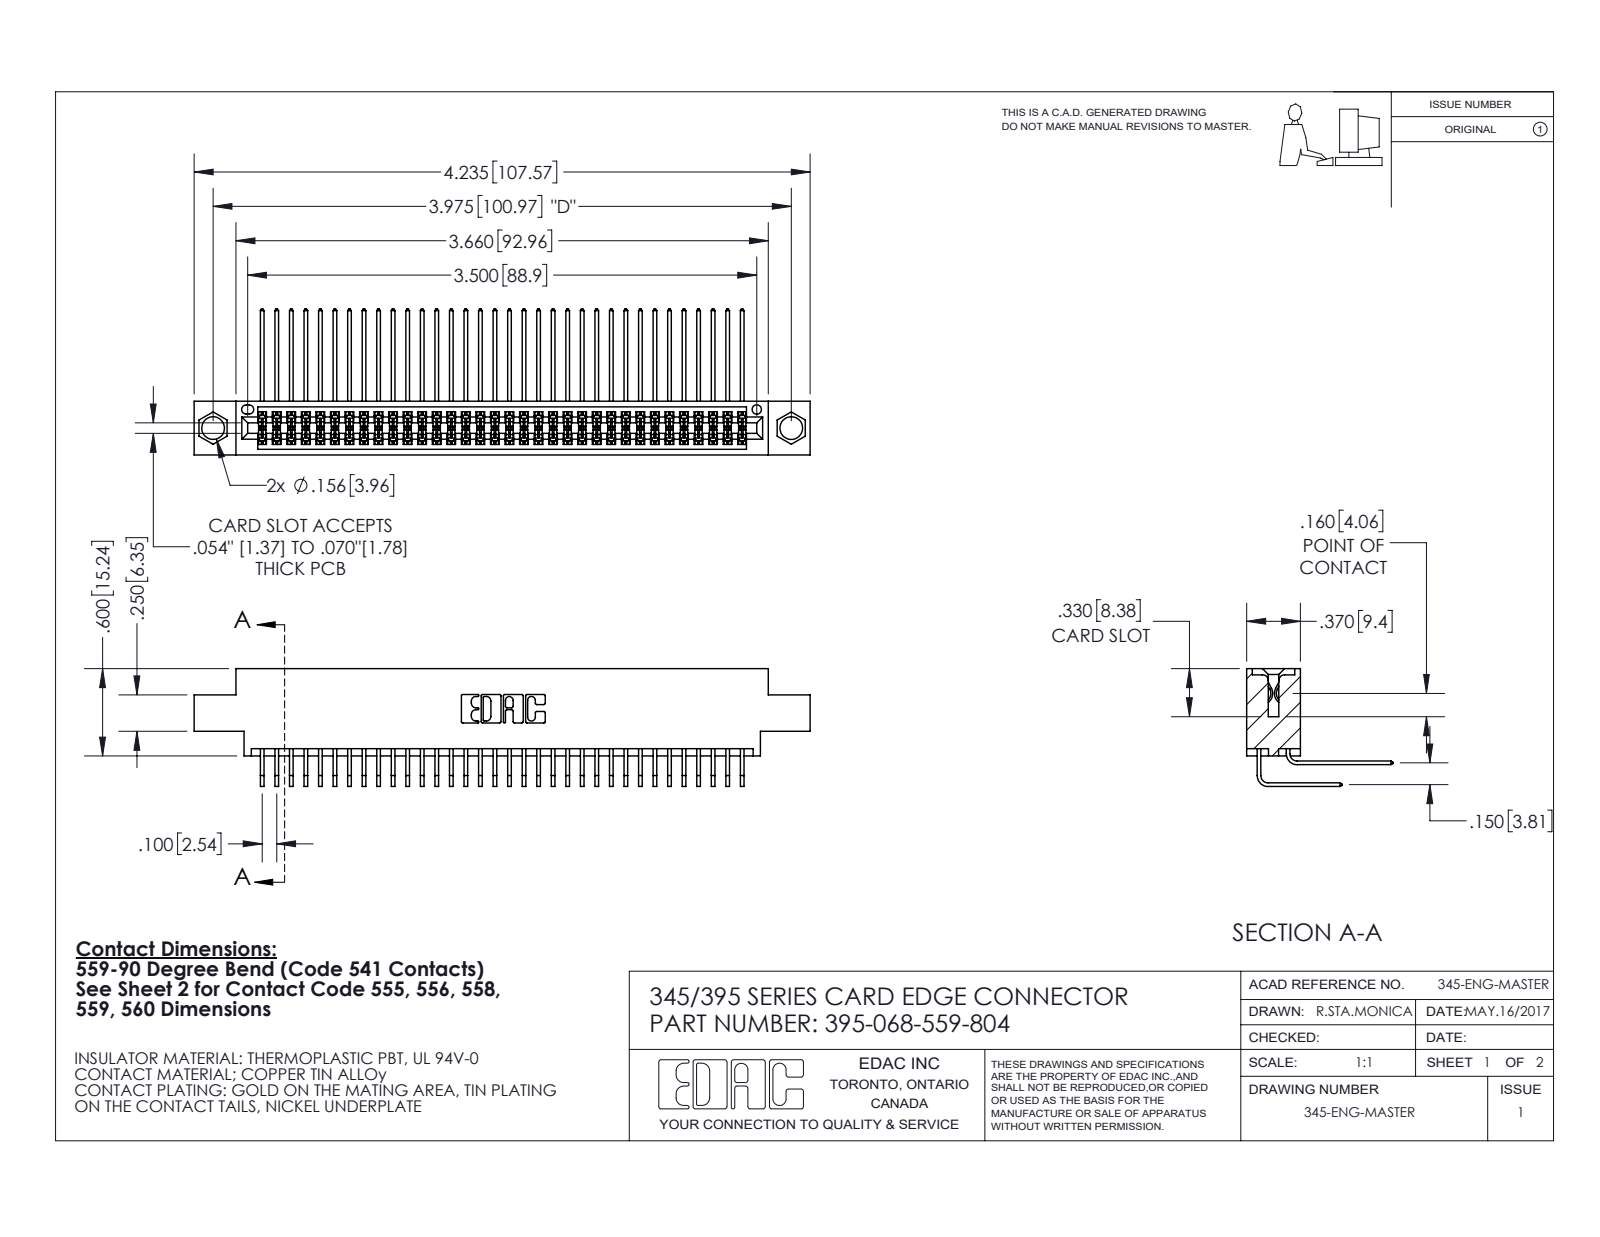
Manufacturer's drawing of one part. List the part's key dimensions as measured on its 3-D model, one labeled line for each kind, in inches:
Part name (STEP PRODUCT): 345-292-001_559 Tail - 2; 395-068-559-804; 345-292-001_558 559 Tail - 1; 345 Part_0.170 Offset - 0.156 Dia-TI
STEP written by: SolidWorks 2020 (CONFIG_CONTROL_DESIGN)
Units: inches
Bodies: 69 solids, 3680 faces (2478 planar, 1202 cylindrical, 0 other)
Overall size (bounding box): 4.235 × 1.005 × 0.809
Volume: 0.644 in³ · Surface area: 26.78 in²
Round holes (diameter × count): ⌀0.156 ×2, ⌀0.064 ×1
Partial cylindrical surfaces — rounded edges, fillets, slot ends (radius × count): R0.006 ×102, R0.01 ×22, R0.007 ×6, R0.031 ×6, R0.026 ×3, R0.014 ×2, R0.019 ×2, R0.022 ×2
Main face-to-face distances: 0.072, 0.298, 0.37, 0.2, 0.098, 0.272, 0.025, 0.225, 0.175, 0.15
Hole centre spacings: 0.27, 3.74, 3.975
